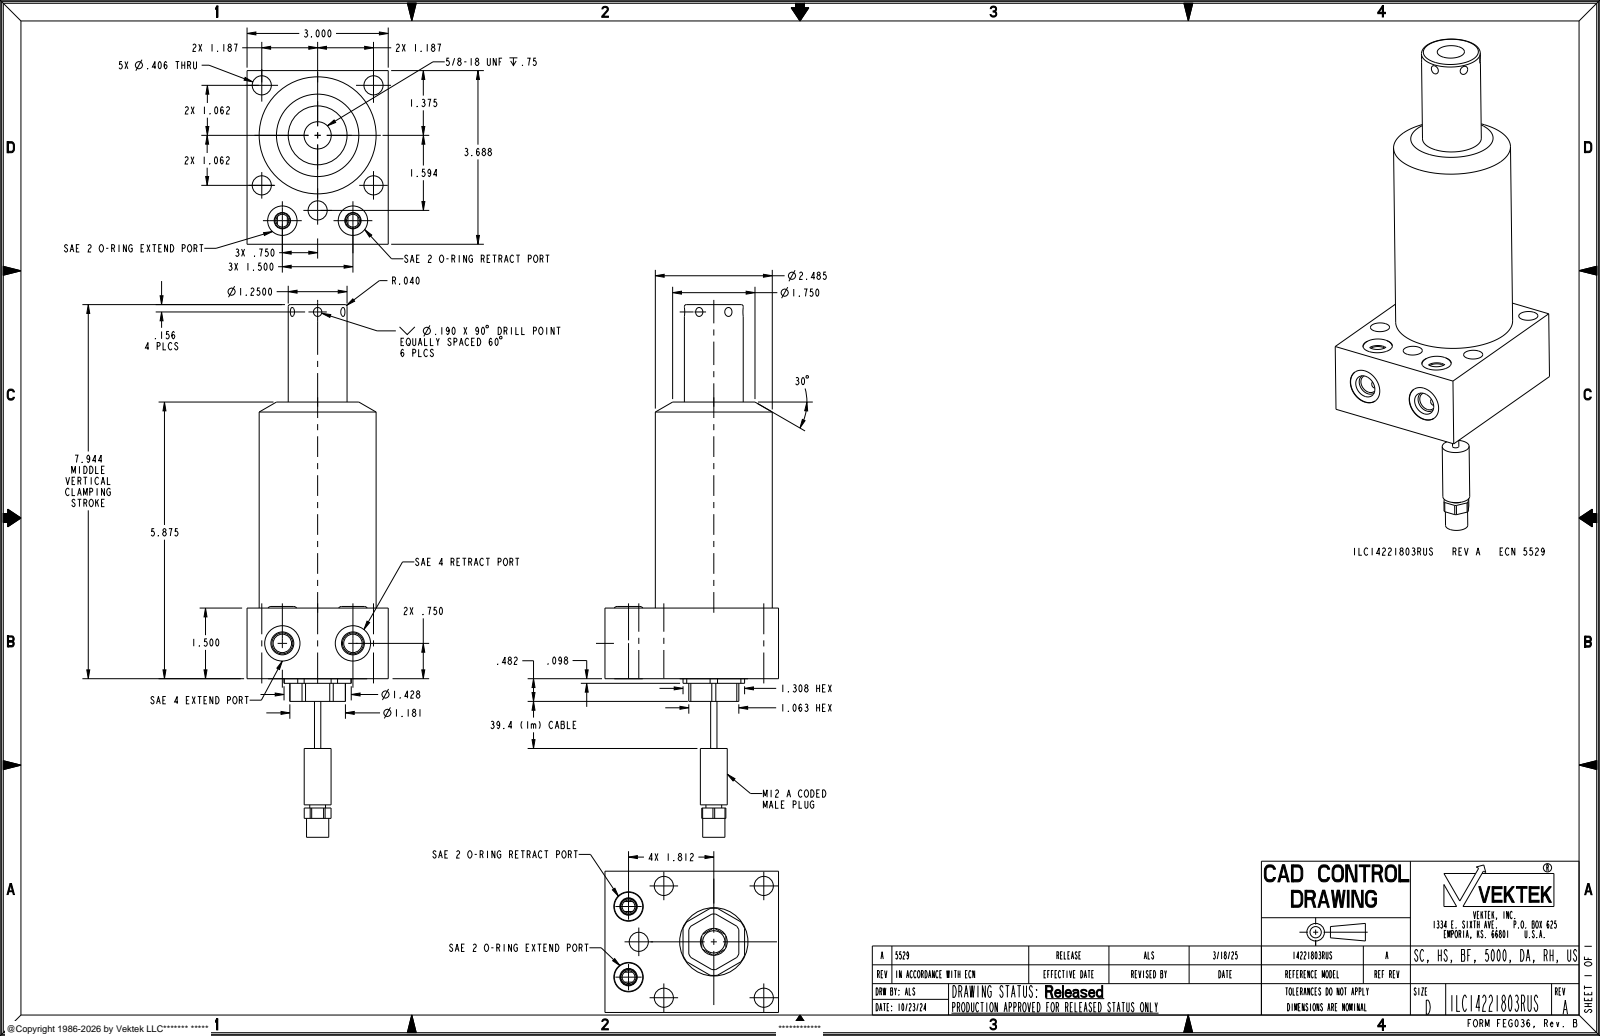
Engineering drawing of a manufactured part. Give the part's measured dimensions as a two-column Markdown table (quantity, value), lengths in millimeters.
| quantity | value |
| --- | --- |
| part name | ILC14221803RUS |
| STEP written by | CREO PARAMETRIC BY PTC INC, 2021164 (AUTOMOTIVE_DESIGN) |
| units | millimeters |
| bodies | 5 solids, 173 faces (49 planar, 70 cylindrical, 54 other) |
| overall size | 287.3 × 93.7 × 76.2 |
| volume | 646 000 mm³ |
| surface area | 69 290 mm² |
| round holes (diameter × count) | 10.3 × 5, 6.9 × 2, 10 × 2, 15.9 × 2, 19.1 × 2, 14.7 × 1 |
| round bosses / shafts (diameter × count) | 63.1 × 1, 36.8 × 1, 31.8 × 1, 15.9 × 1, 14.5 × 1, 12 × 1, 8.5 × 1, 3.4 × 1 |
| partial cylindrical surfaces (radius × count) | 15 × 1, 18.1 × 1 |
| main face-to-face distances | 76.2, 38.1, 93.7, 149.2, 111.1, 12.2, 50.3, 161.5, 2.7, 35.4 |
| hole center spacings | 40.5, 19.8, 22, 33, 38.1, 49.8, 52.8, 53.9 |
